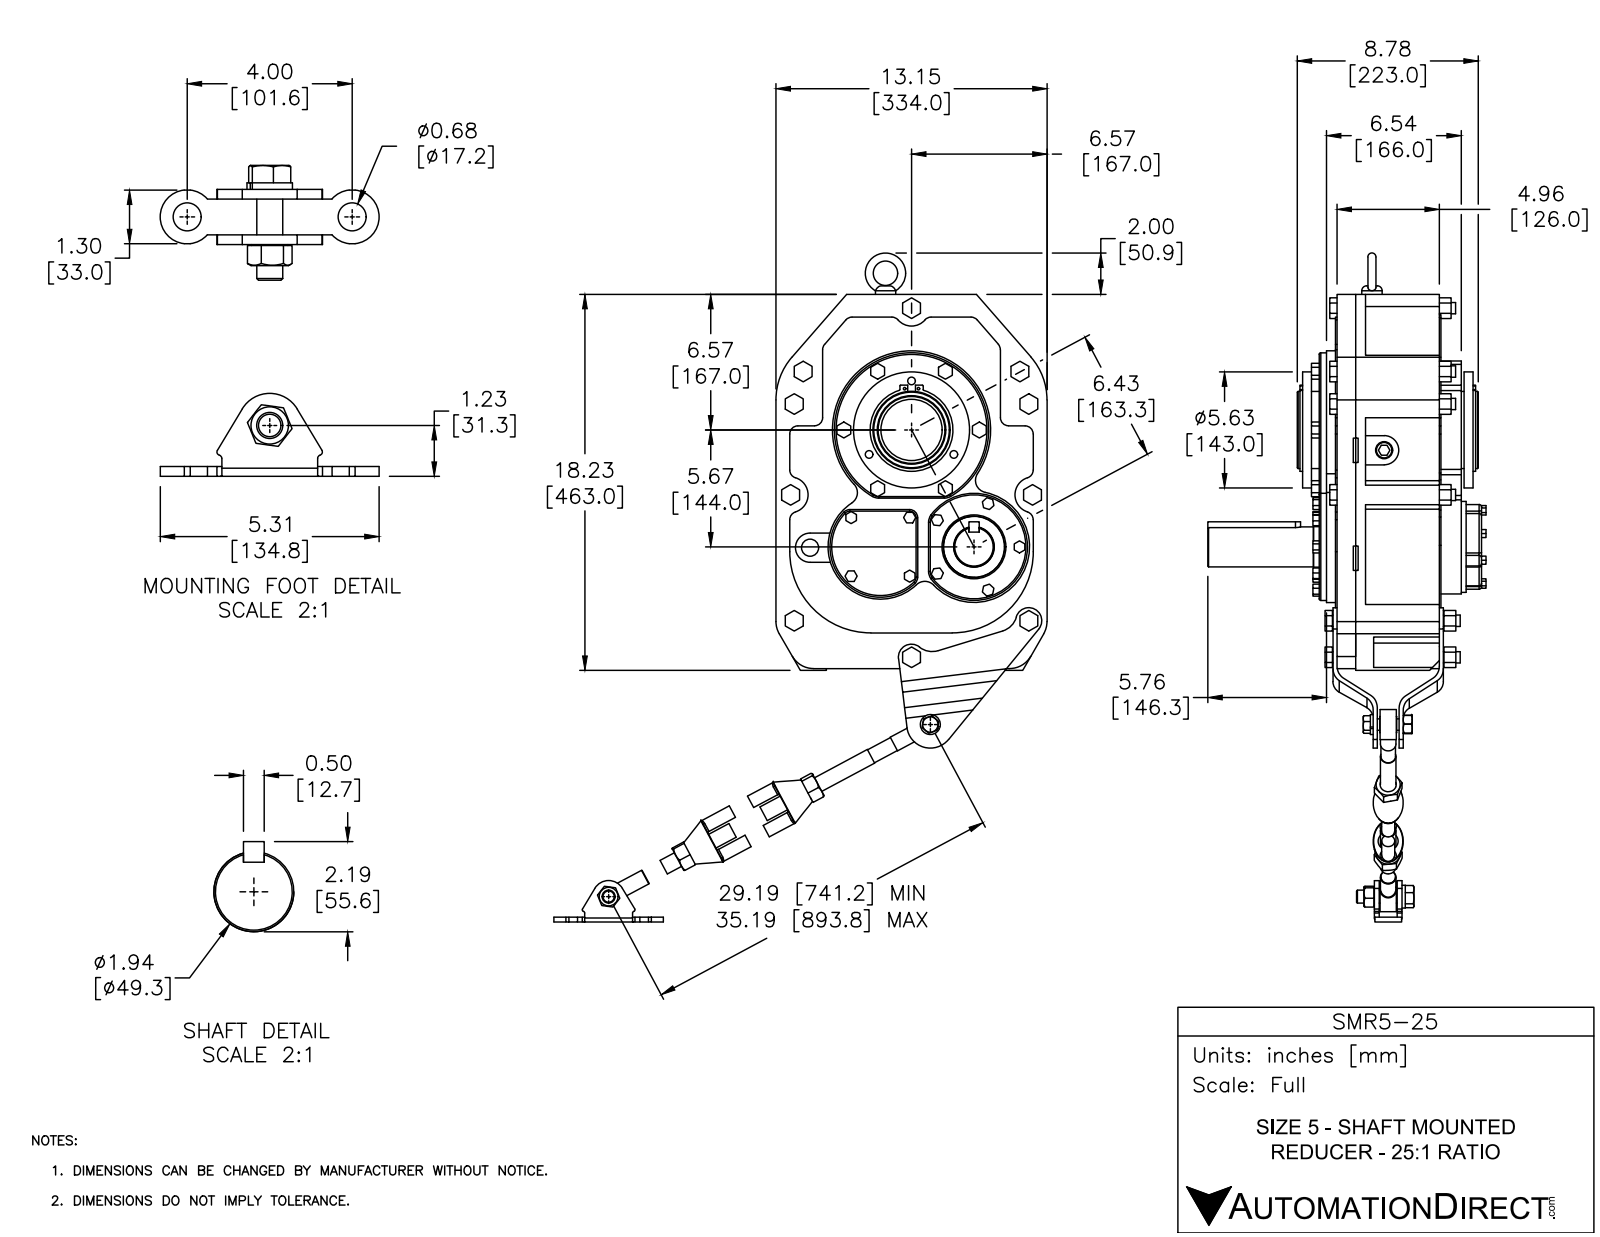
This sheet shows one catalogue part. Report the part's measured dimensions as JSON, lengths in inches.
{"part_name": "SMR5-TA_5; SMR5-25_REDUCER; SMR5-TA_1; SMR5-TA_2 (+4 more)", "step_written_by": "SolidWorks 2016 (AUTOMOTIVE_DESIGN)", "units": "inches", "bodies": {"solids": 74, "faces": 1347, "planar": 740, "cylindrical": 451, "other": 156}, "overall_size": [34.462, 27.708, 13.494], "volume_in3": 1200, "surface_area_in2": 2473, "round_holes": [[0.591, 12], [0.531, 8], [0.827, 5], [0.368, 3], [0.118, 2], [0.677, 2], [0.689, 2], [0.787, 2], [0.551, 1], [0.559, 1], [0.571, 1], [0.63, 1]], "round_bosses_or_shafts": [[0.551, 10], [0.75, 4], [1.457, 2], [0.711, 2], [0.63, 2], [7.48, 1], [5.63, 1], [5.197, 1]], "partial_cylinders_radius": [[0.394, 31], [0.591, 19], [0.118, 12], [0.079, 8], [0.866, 5], [0.039, 4], [0.276, 4], [0.709, 4]], "face_to_face_distances": [0.984, 0.079, 5.118, 5.039, 1.417, 0.512, 0.433, 0.866, 6.024, 0.906], "hole_center_spacings": [3.661, 5.178, 2.374, 2.984, 4.112, 10.512, 0.503, 1.5]}
